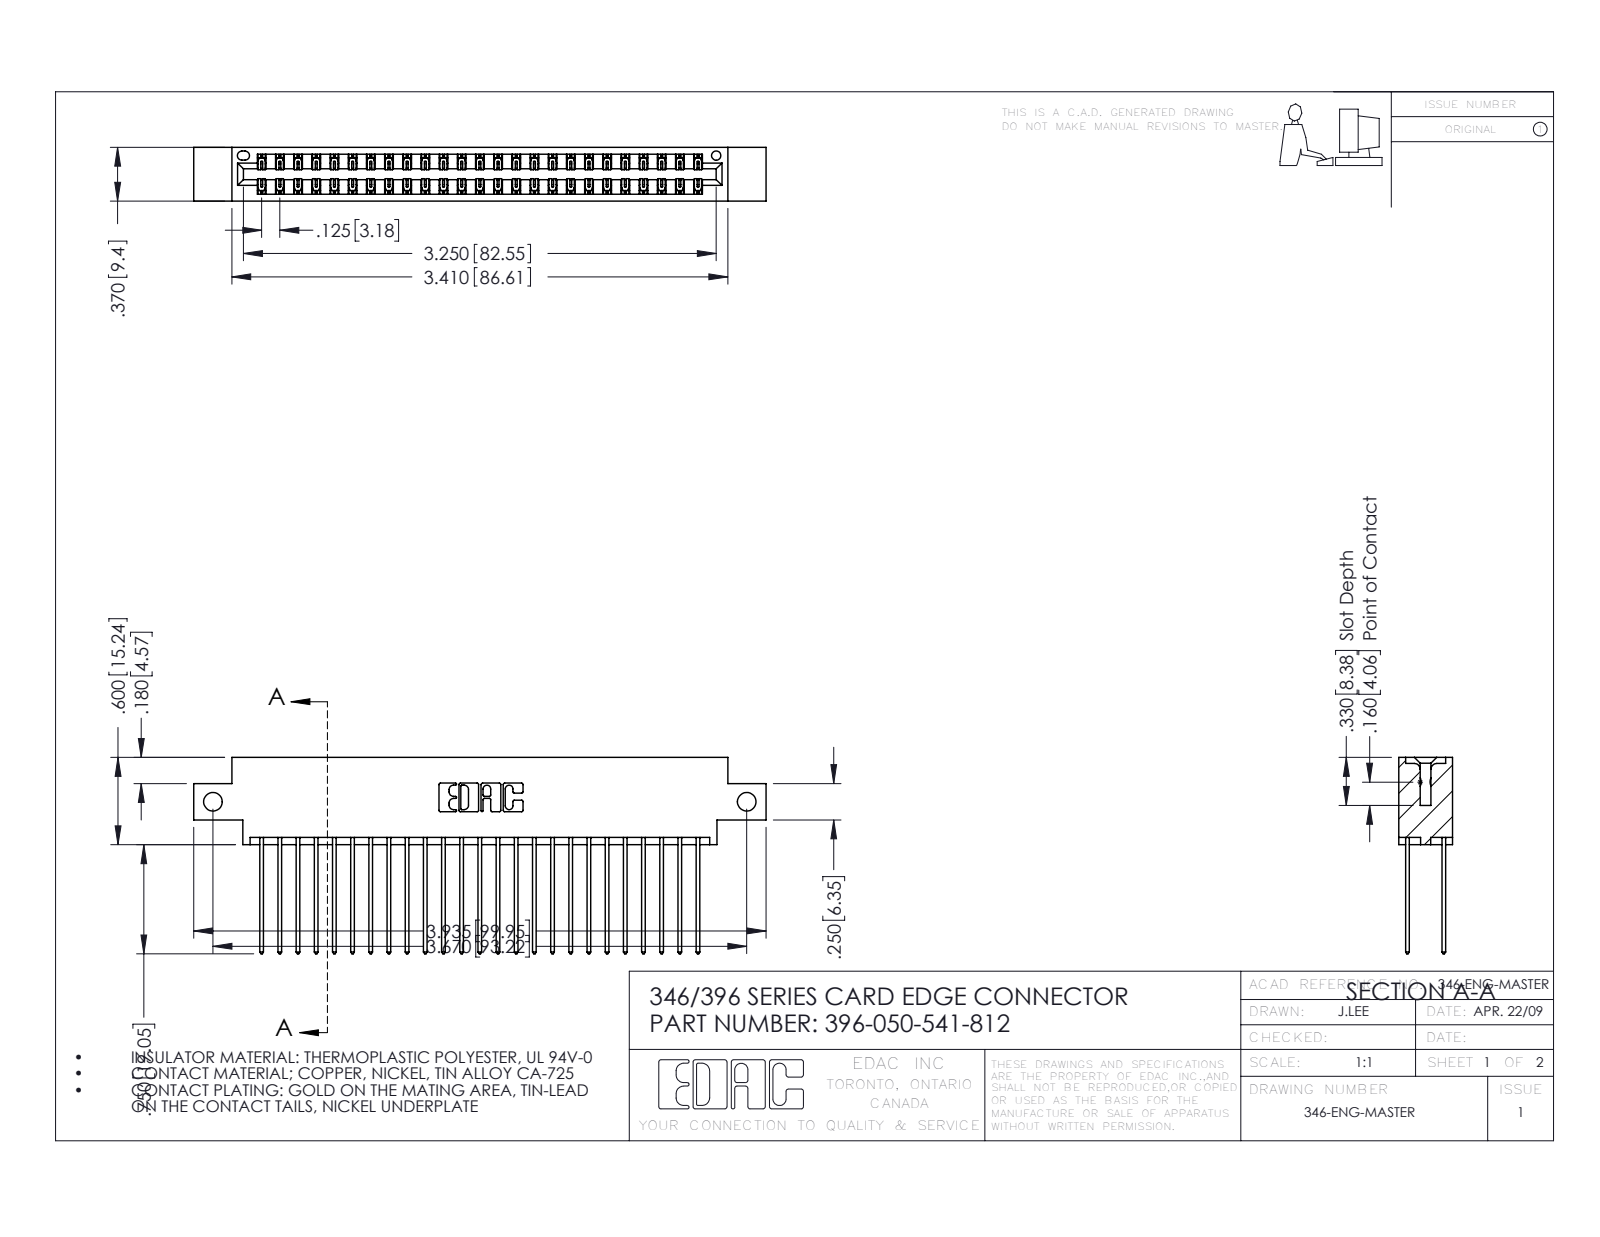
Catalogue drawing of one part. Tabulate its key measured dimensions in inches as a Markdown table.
| quantity | value |
| --- | --- |
| part name | 346 Part_0.170 Offset - Side Mount; 345-292-001_345-293-141; 396-050-541-812 |
| STEP written by | SolidWorks 2016 (CONFIG_CONTROL_DESIGN) |
| units | inches |
| bodies | 51 solids, 2726 faces (1830 planar, 896 cylindrical, 0 other) |
| overall size | 3.935 × 1.35 × 0.37 |
| volume | 0.589 in³ |
| surface area | 22.36 in² |
| round holes (diameter × count) | 0.128 × 2, 0.064 × 1 |
| partial cylindrical surfaces (radius × count) | 0.006 × 75, 0.01 × 50, 0.01 × 22, 0.007 × 6, 0.031 × 6, 0.026 × 3, 0.014 × 2, 0.022 × 2 |
| main face-to-face distances | 0.048, 0.322, 0.25, 0.072, 0.298, 0.025, 0.37, 0.275, 0.225, 0.148 |
| hole center spacings | 3.67 |
